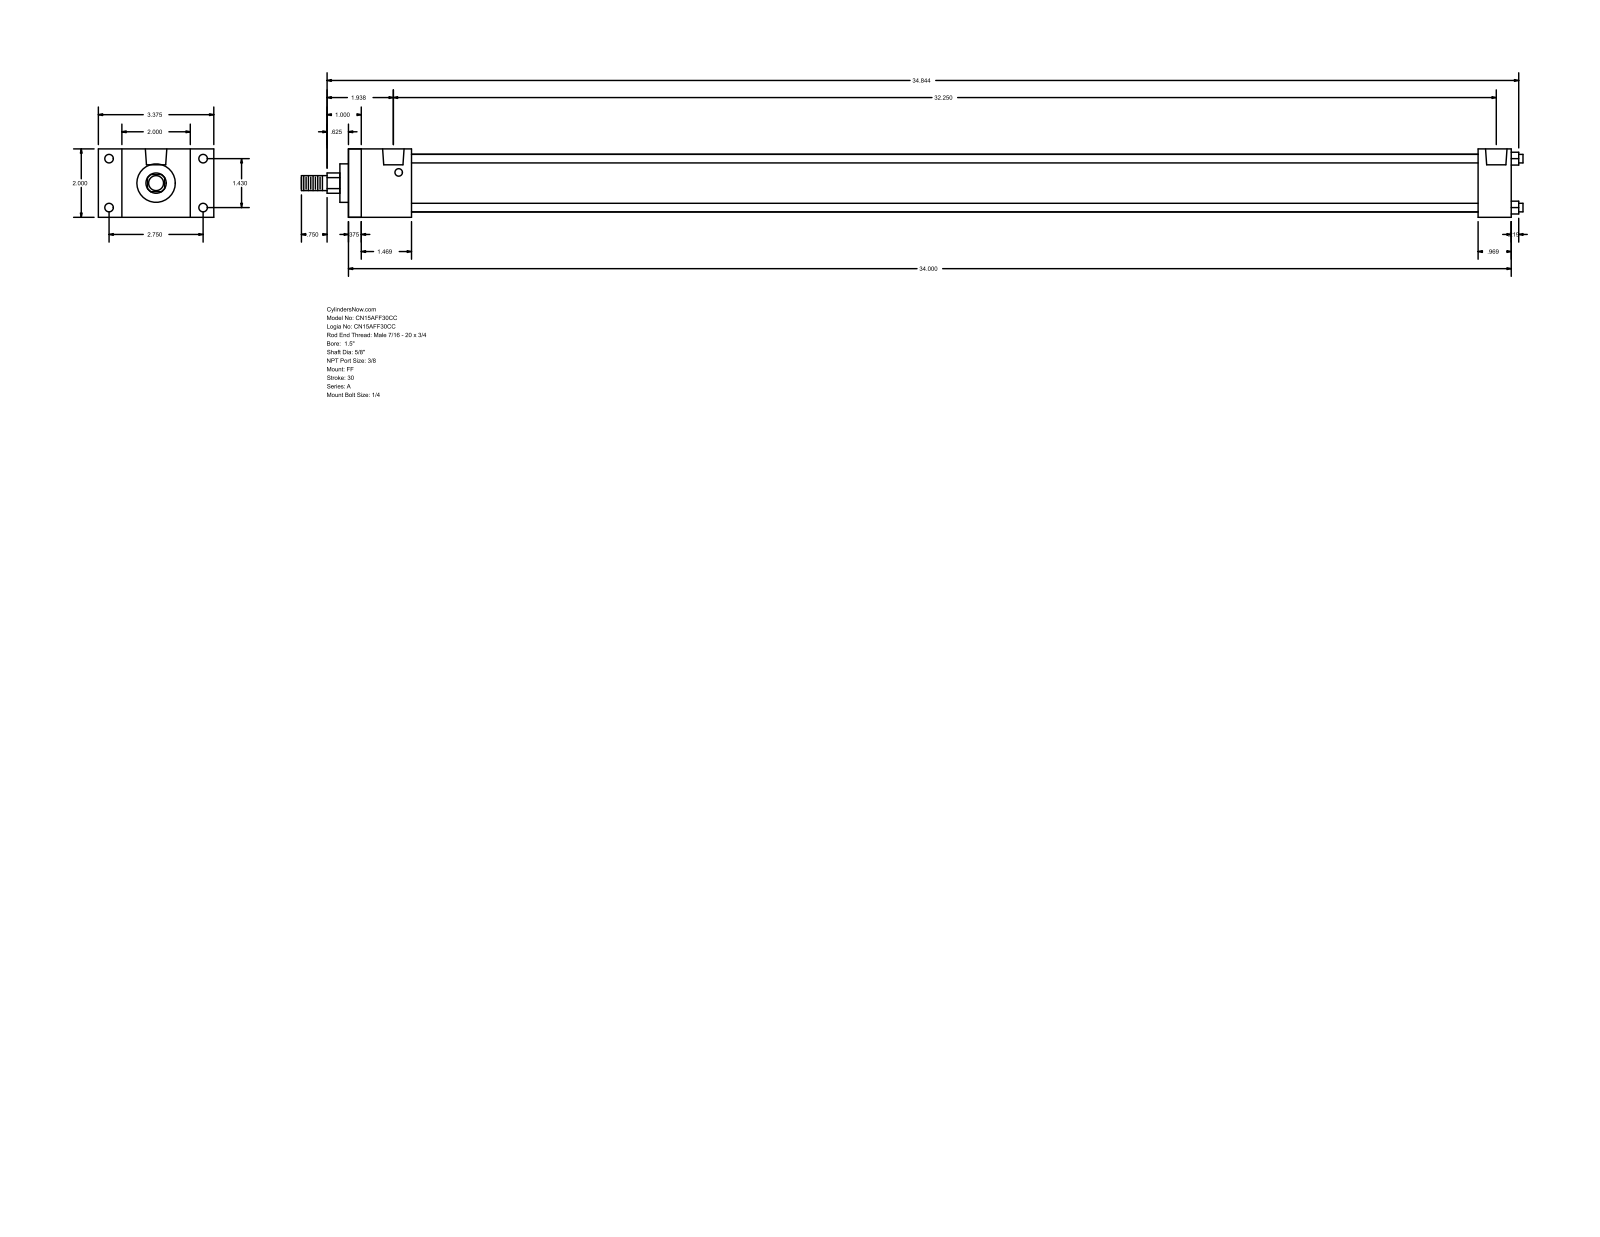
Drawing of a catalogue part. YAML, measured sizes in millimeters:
part_name: "A_FF__0150_0.625"
step_written_by: "GSSL Pune (CONFIG_CONTROL_DESIGN)"
units: millimeters
bodies: {solids: 0, faces: 92, planar: 64, cylindrical: 28, other: 0}
overall_size: [907.26, 85.72, 50.8]
round_holes:
  - {diameter: 5.56, count: 4}
  - {diameter: 6.35, count: 4}
  - {diameter: 15.93, count: 2}
round_bosses_or_shafts:
  - {diameter: 6.35, count: 4}
  - {diameter: 42.93, count: 1}
  - {diameter: 28.57, count: 1}
  - {diameter: 15.88, count: 1}
  - {diameter: 11.11, count: 1}
partial_cylinders:
  - {radius: 7.54, count: 1}
face_to_face_distances: [50.8, 863.6, 9.52, 854.08, 46.83, 838.99, 37.31, 829.47, 792.16, 816.77]
hole_center_spacings: [3.97, 36.32, 69.84, 78.72, 811.21, 815.18, 819.15]
